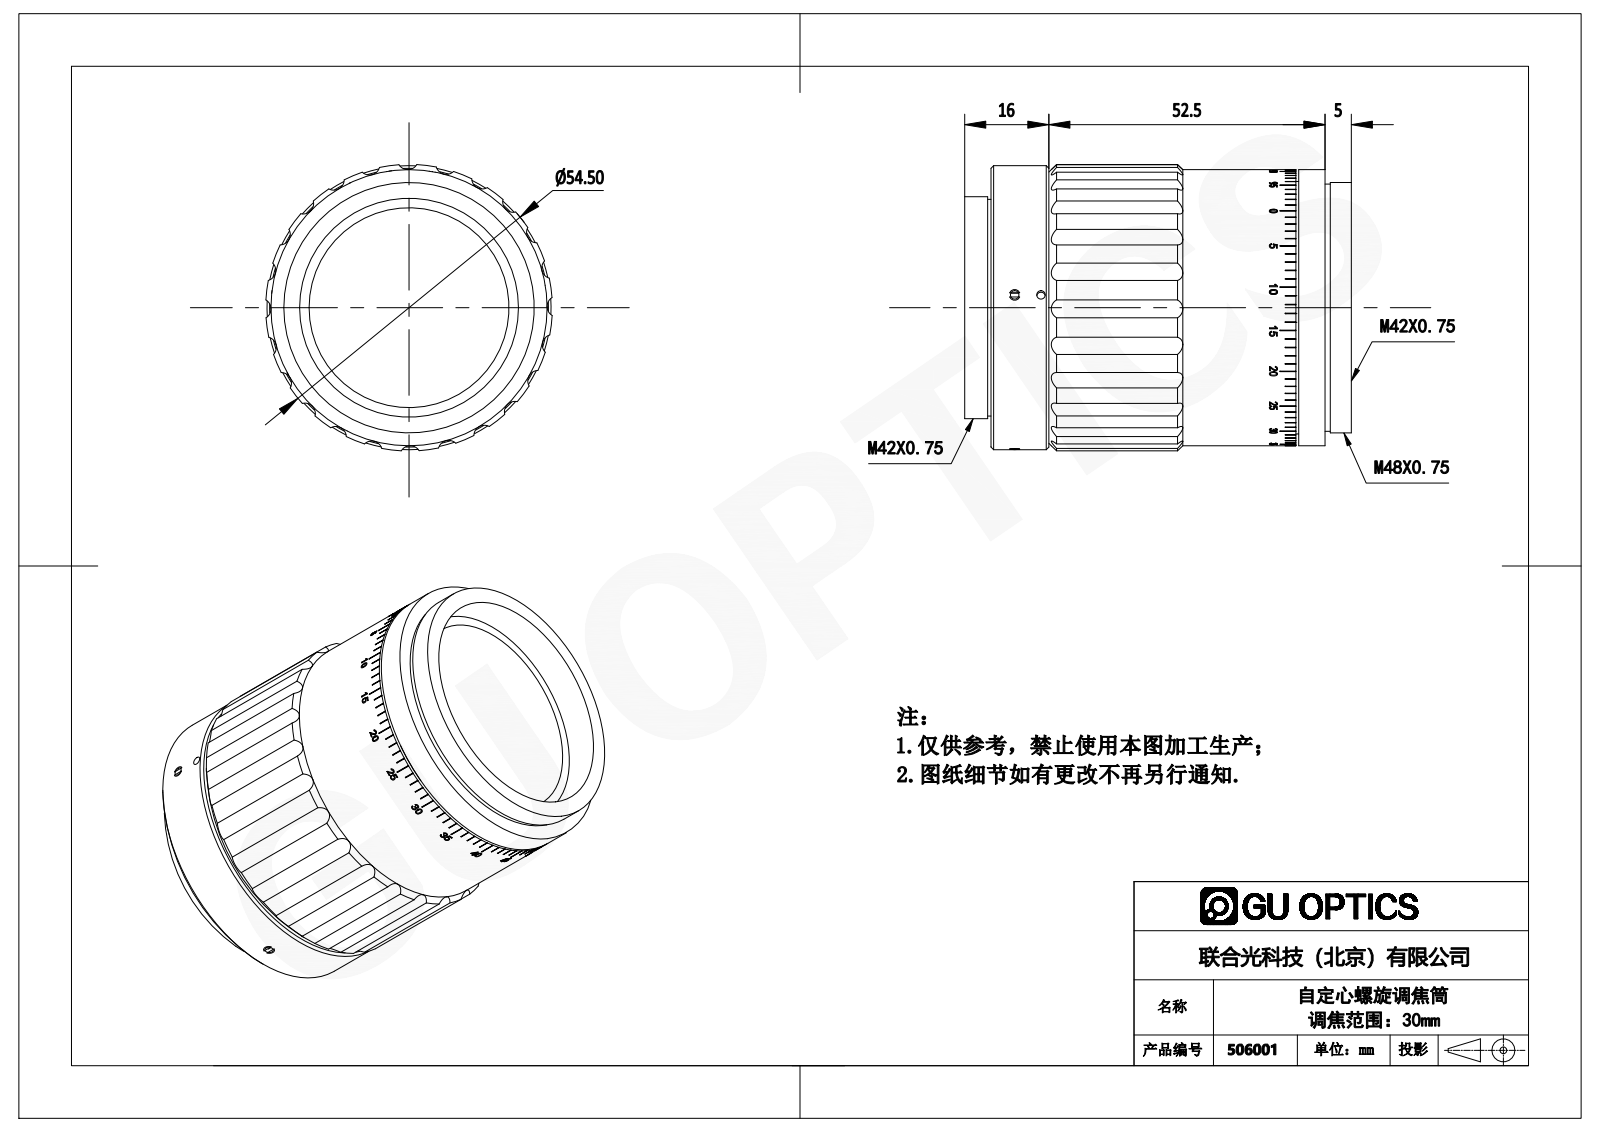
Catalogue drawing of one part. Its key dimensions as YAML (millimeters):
part_name: "506000自定心连动圈; 506001"
step_written_by: "SolidWorks 2016 (AUTOMOTIVE_DESIGN)"
units: millimeters
bodies: {solids: 8, faces: 1069, planar: 347, cylindrical: 380, other: 342}
overall_size: [73.5, 54.42, 54.42]
volume: 67723
surface_area: 60974
round_holes:
  - {diameter: 1.6, count: 5}
  - {diameter: 2.1, count: 3}
  - {diameter: 38, count: 1}
  - {diameter: 41.6, count: 1}
  - {diameter: 44, count: 1}
  - {diameter: 44.5, count: 1}
  - {diameter: 44.7, count: 1}
  - {diameter: 47.7, count: 1}
  - {diameter: 49.5, count: 1}
  - {diameter: 51, count: 1}
round_bosses_or_shafts:
  - {diameter: 2.06, count: 4}
  - {diameter: 2, count: 4}
  - {diameter: 54, count: 1}
  - {diameter: 52.5, count: 1}
  - {diameter: 50.6, count: 1}
  - {diameter: 48, count: 1}
  - {diameter: 47.6, count: 1}
  - {diameter: 47.5, count: 1}
partial_cylinders:
  - {radius: 2, count: 24}
  - {radius: 22.25, count: 4}
  - {radius: 22, count: 3}
  - {radius: 26.23, count: 1}
  - {radius: 27.25, count: 1}
face_to_face_distances: [12, 2, 5, 10, 14, 1, 56.5, 63.5, 68.5, 51.54]
hole_center_spacings: [5]
